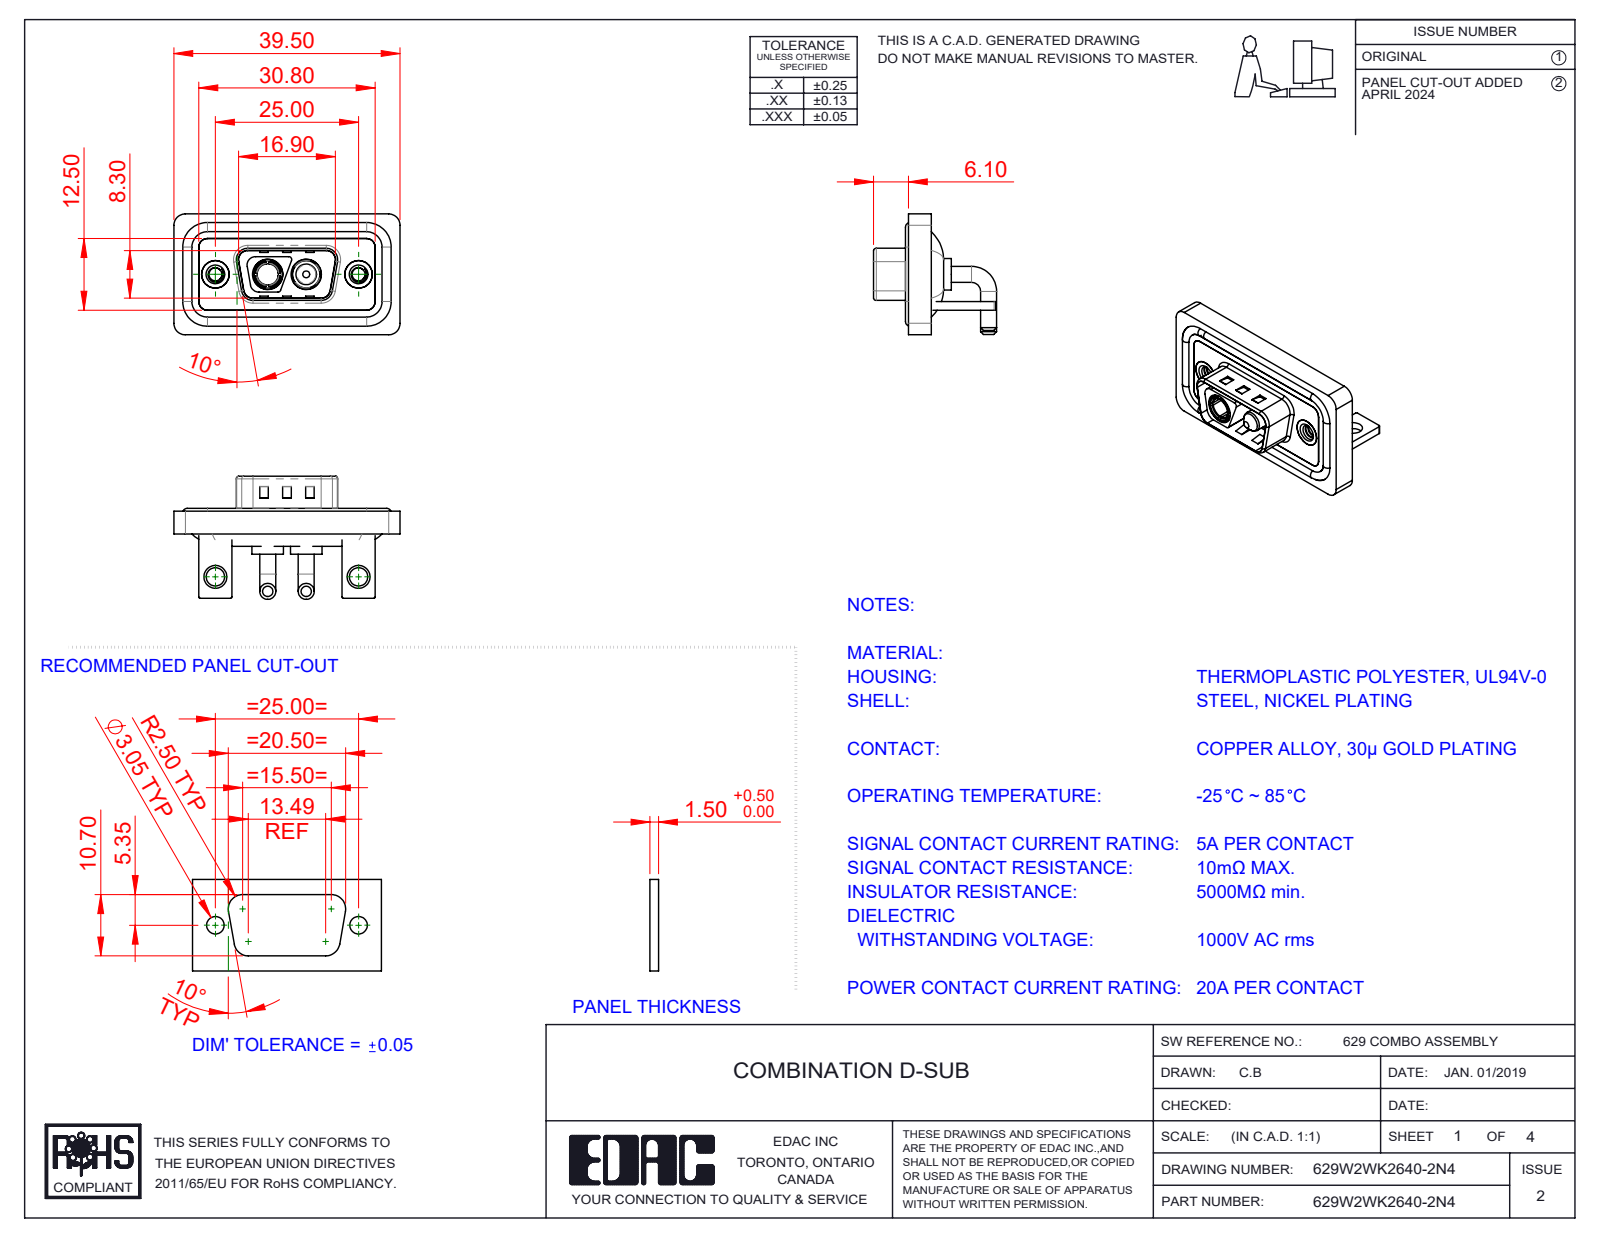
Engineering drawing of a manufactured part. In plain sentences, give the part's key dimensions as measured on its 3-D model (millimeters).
The part is named "629Combo Threaded Rivet_3; Power Pin_20A RA; 629Combo Stabilizer Bracket; 629Combo Shell Rear_09 Contacts (+5 more)". Its 3-D file was written by "SolidWorks 2023 (CONFIG_CONTROL_DESIGN)". It is 13 solids with 582 faces: 209 planar, 249 cylindrical and 124 other. Overall it measures 39.5 by 21.5 by 21.1 millimeters. Its volume is 4 960 cubic millimeters and its surface area 8 119 square millimeters. Round holes: 2 of diameter 2.26, 2 of diameter 3.2, 2 of diameter 4, 2 of diameter 4.8, 2 of diameter 4.85, 2 of diameter 5, 2 of diameter 5.3, 1 of diameter 3.7. Round bosses or shafts: 4 of diameter 2.8, 4 of diameter 1.6, 2 of diameter 5.5, 2 of diameter 5.2, 2 of diameter 4.9, 2 of diameter 4.75, 2 of diameter 3.75, 1 of diameter 4.96. Partial cylindrical surfaces (rounded edges, fillets, slot ends): 20 of radius 1.5, 19 of radius 2, 16 of radius 0.25, 11 of radius 0.5, 8 of radius 1.6, 4 of radius 0.6, 4 of radius 0.65, 4 of radius 0.9. The main face-to-face distances are 0.4, 1.5, 2.9, 0.8, 1.1, 1.2, 2.1, 1.6, 3.7, 2.5. The hole center spacings are 9.14, 15.86, 25, 6.72.
